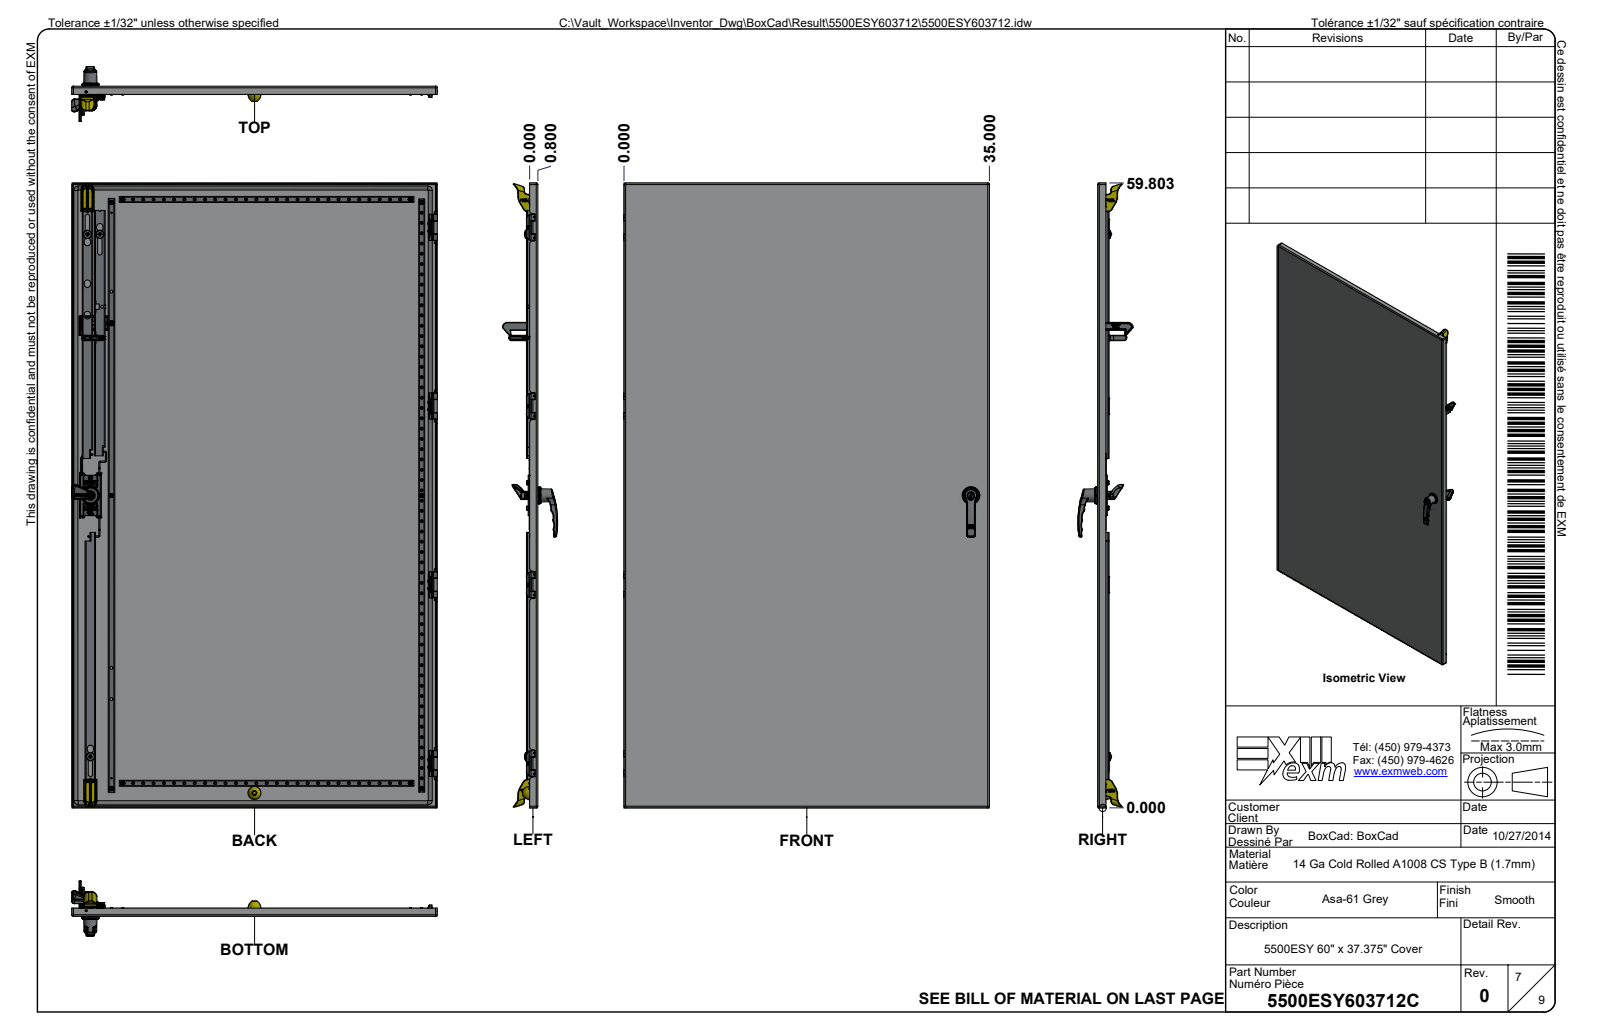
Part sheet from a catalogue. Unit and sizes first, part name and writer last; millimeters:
Units: millimetres
Overall size (bounding box): 1524 × 949.8 × 380.6
Round holes (diameter × count): ⌀4.2 ×166, ⌀0.8 ×28, ⌀8 ×22, ⌀5.1 ×19, ⌀1.1 ×16, ⌀5 ×12, ⌀6.8 ×12, ⌀7.9 ×10, ⌀4.5 ×8, ⌀6.9 ×8, ⌀7.4 ×6, ⌀12.7 ×5
Round bosses / shafts (diameter × count): ⌀6 ×166, ⌀0.8 ×28, ⌀5.9 ×23, ⌀4.5 ×16, ⌀1 ×16, ⌀9.5 ×12, ⌀18.2 ×8, ⌀7.9 ×8
Partial cylindrical surfaces — rounded edges, fillets, slot ends (radius × count): R0.5 ×582, R0.3 ×418, R1 ×312, R0.2 ×152, R2 ×73, R1.5 ×66, R4 ×61, R0.5 ×60
Main face-to-face distances: 1.7, 331.5, 329.8, 333.2, 23.9, 22.2, 307.6, 309.3, 26.6, 24.9
Hole centre spacings: 434.4, 868.7, 8.9, 18.7, 26.7, 35.2, 434.4, 1303.1
Volume: 12 340 000 mm³ · Surface area: 12 870 000 mm²
Bodies: 135 solids, 25527 faces (6659 planar, 7015 cylindrical, 11853 other)
Part name (STEP PRODUCT): 5500ESY603712; 5500ESY603712B; 5500ESY603712B-P; STK-Q-16005 (+8 more)
STEP written by: Autodesk Inventor 2024 (AUTOMOTIVE_DESIGN)
